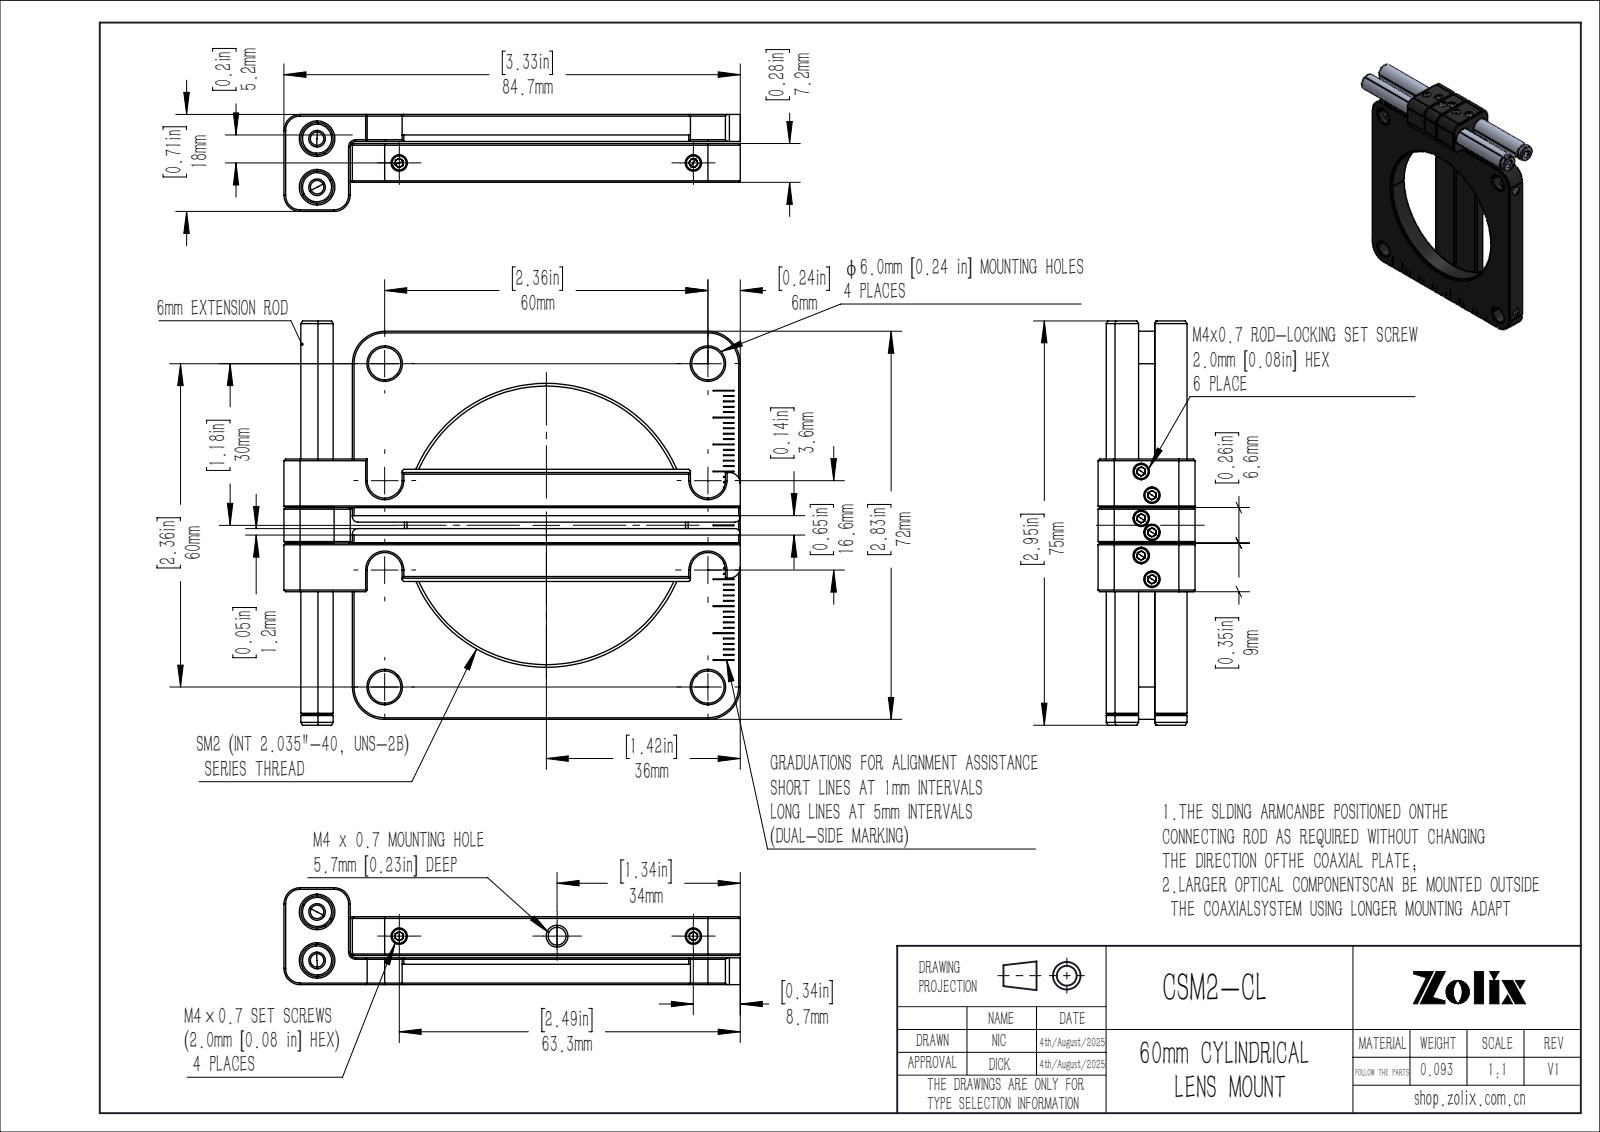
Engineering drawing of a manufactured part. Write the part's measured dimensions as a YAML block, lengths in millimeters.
part_name: "CSM2-CL"
step_written_by: "SolidWorks 2020 (CONFIG_CONTROL_DESIGN)"
units: millimeters
bodies: {solids: 17, faces: 1403, planar: 987, cylindrical: 126, other: 290}
overall_size: [84.7, 75, 18]
volume: 34458
surface_area: 22012
round_holes:
  - {diameter: 2.5, count: 10}
  - {diameter: 6, count: 6}
  - {diameter: 3.3, count: 1}
  - {diameter: 51.69, count: 1}
round_bosses_or_shafts:
  - {diameter: 3, count: 8}
partial_cylinders:
  - {radius: 1, count: 5}
  - {radius: 0.3, count: 4}
  - {radius: 3, count: 4}
  - {radius: 3.25, count: 4}
  - {radius: 6, count: 4}
  - {radius: 0.4, count: 2}
  - {radius: 2, count: 2}
face_to_face_distances: [7.2, 0.4, 7.6, 5.4, 12.6, 5, 1.2, 6.6, 32.7, 39.3]
hole_center_spacings: [42.43, 60, 4.74, 4.83, 6.9, 8.7, 11.48, 15.6]
